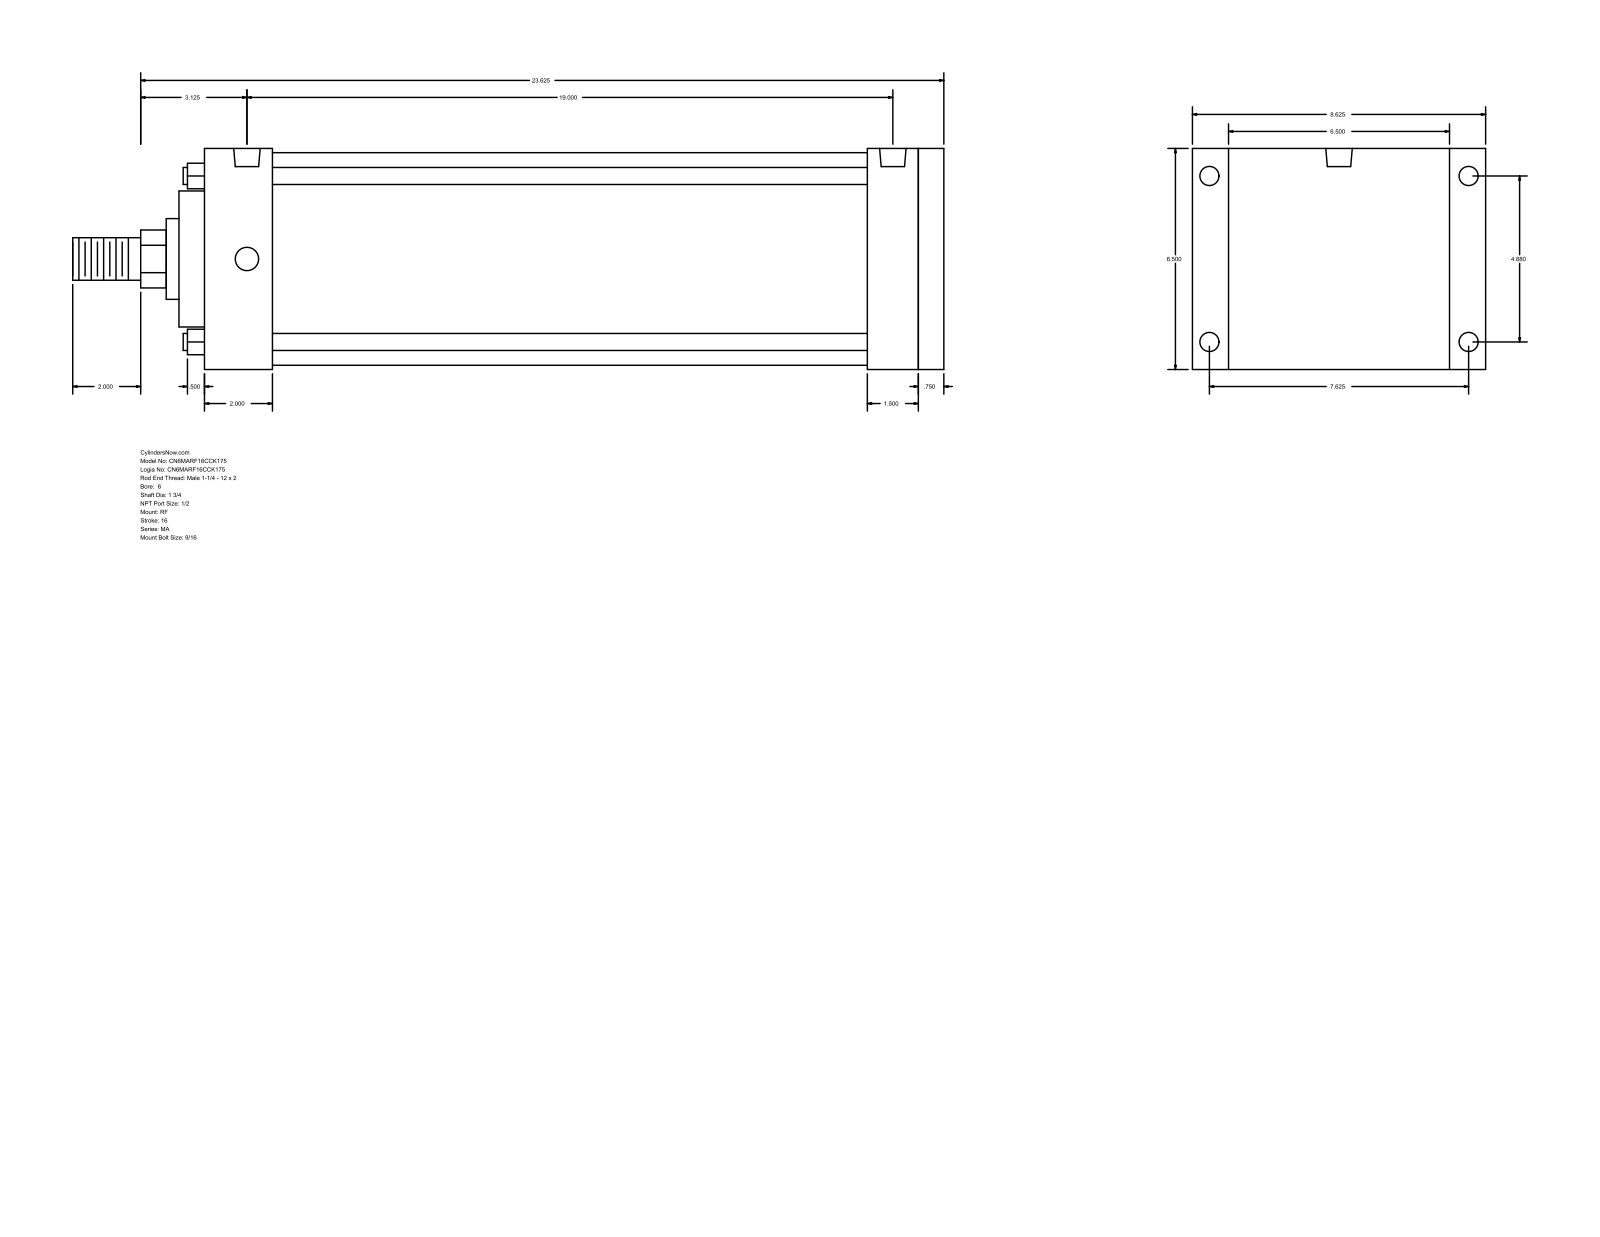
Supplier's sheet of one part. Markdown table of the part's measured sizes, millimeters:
| quantity | value |
| --- | --- |
| part name | MA_RF__0600_1.75 |
| STEP written by | GSSL Pune (CONFIG_CONTROL_DESIGN) |
| units | millimeters |
| bodies | 0 solids, 94 faces (65 planar, 29 cylindrical, 0 other) |
| overall size | 650.88 × 219.07 × 165.1 |
| round holes (diameter × count) | 14.29 × 4, 17.46 × 4, 19.77 × 2 |
| round bosses / shafts (diameter × count) | 12.7 × 4, 158.75 × 1, 101.6 × 1, 60.33 × 1, 44.45 × 1, 31.75 × 1 |
| partial cylindrical surfaces (radius × count) | 21.63 × 1 |
| main face-to-face distances | 165.1, 552.46, 533.4, 19.06, 38.1, 50.8, 19.05, 482.6, 501.66, 495.3 |
| hole center spacings | 123.96, 193.68, 229.95, 482.6 |
